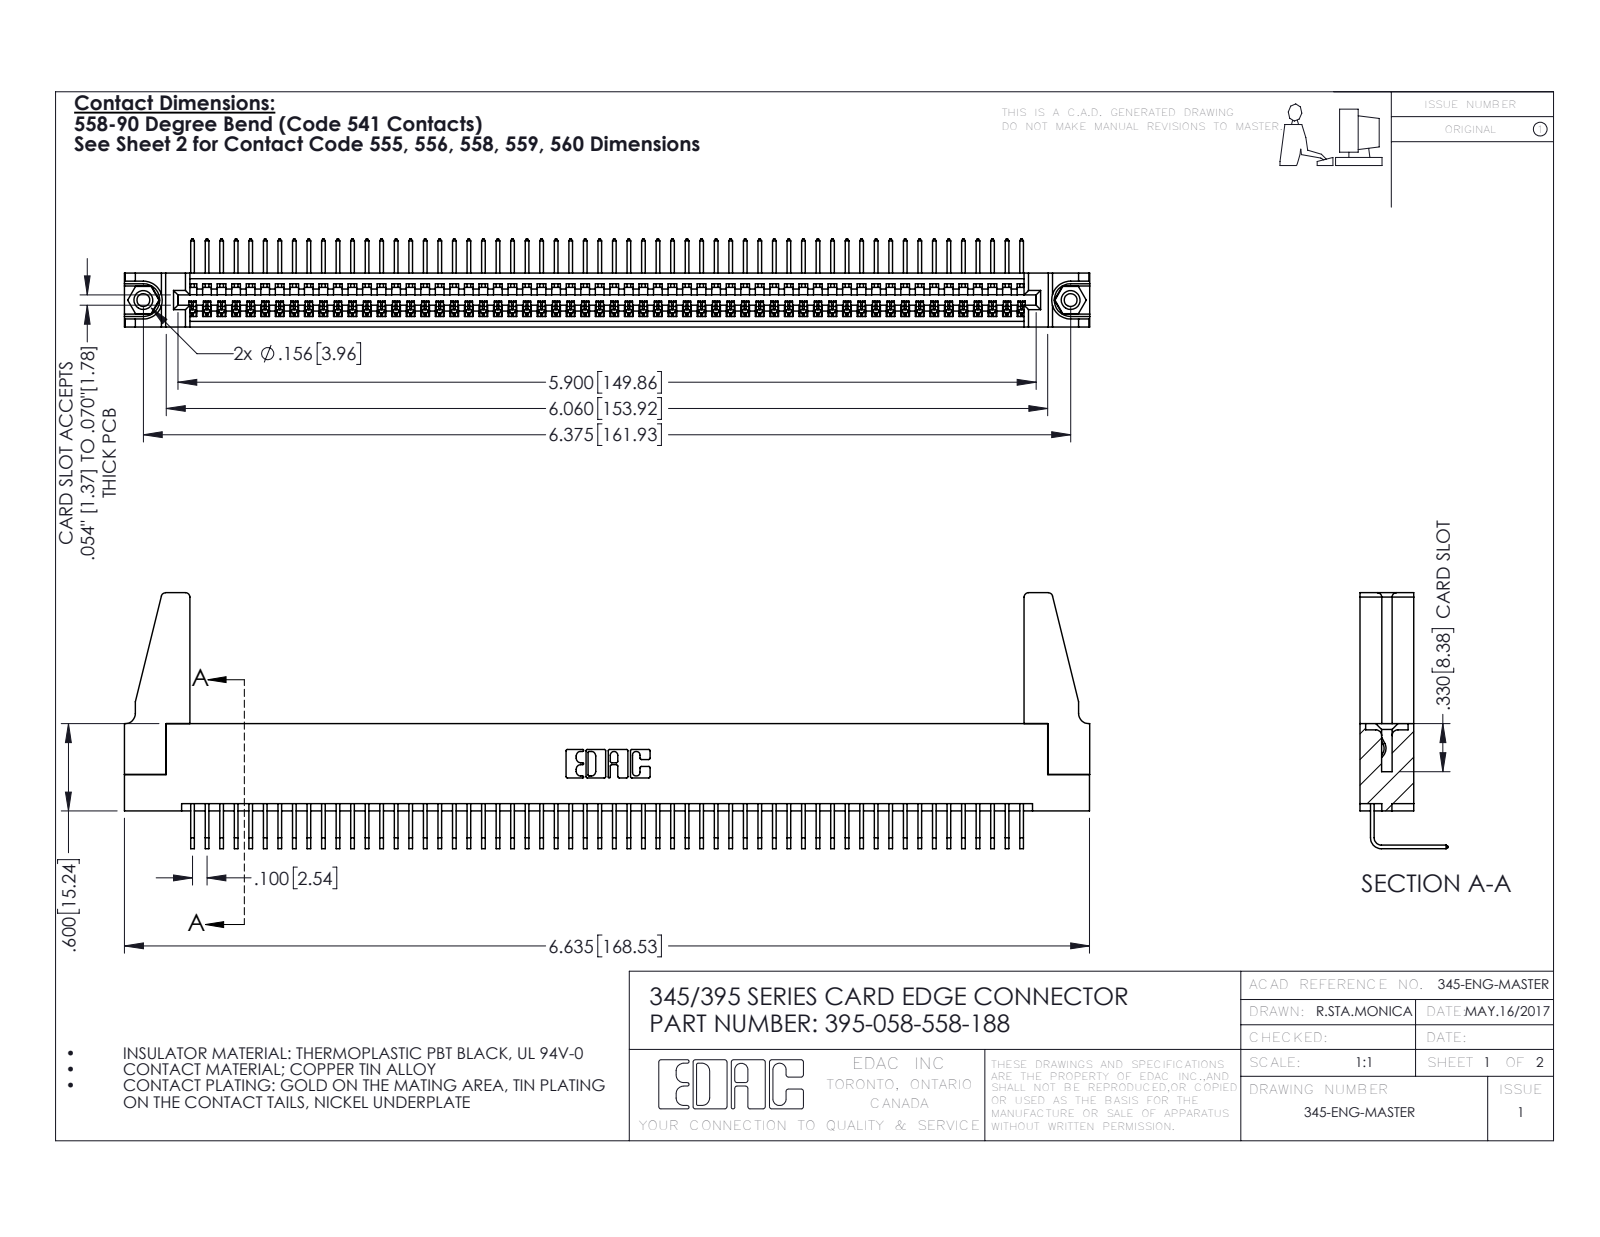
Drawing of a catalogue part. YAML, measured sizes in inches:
part_name: "345 Part_Flush Mounting Lugs - 0.156 Dia-TH; 345-250-001_345-250-001-102; 395-058-558-188; 345-220-078_345-220-088 (+1 more)"
step_written_by: "SolidWorks 2016 (CONFIG_CONTROL_DESIGN)"
units: inches
bodies: {solids: 63, faces: 3730, planar: 2588, cylindrical: 1126, other: 16}
overall_size: [6.636, 1.759, 0.605]
volume: 1.195
surface_area: 40.59
round_holes:
  - {diameter: 0.089, count: 2}
  - {diameter: 0.125, count: 2}
  - {diameter: 0.156, count: 2}
  - {diameter: 0.064, count: 1}
round_bosses_or_shafts:
  - {diameter: 0.155, count: 2}
partial_cylinders:
  - {radius: 0.006, count: 116}
  - {radius: 0.01, count: 22}
  - {radius: 0.03, count: 8}
  - {radius: 0.007, count: 6}
  - {radius: 0.031, count: 6}
  - {radius: 0.026, count: 3}
  - {radius: 0.031, count: 2}
  - {radius: 0.04, count: 2}
face_to_face_distances: [0.072, 0.298, 0.37, 0.2, 0.098, 0.272, 0.025, 0.225, 0.149, 0.072]
hole_center_spacings: [0.27, 6.139, 6.375]
